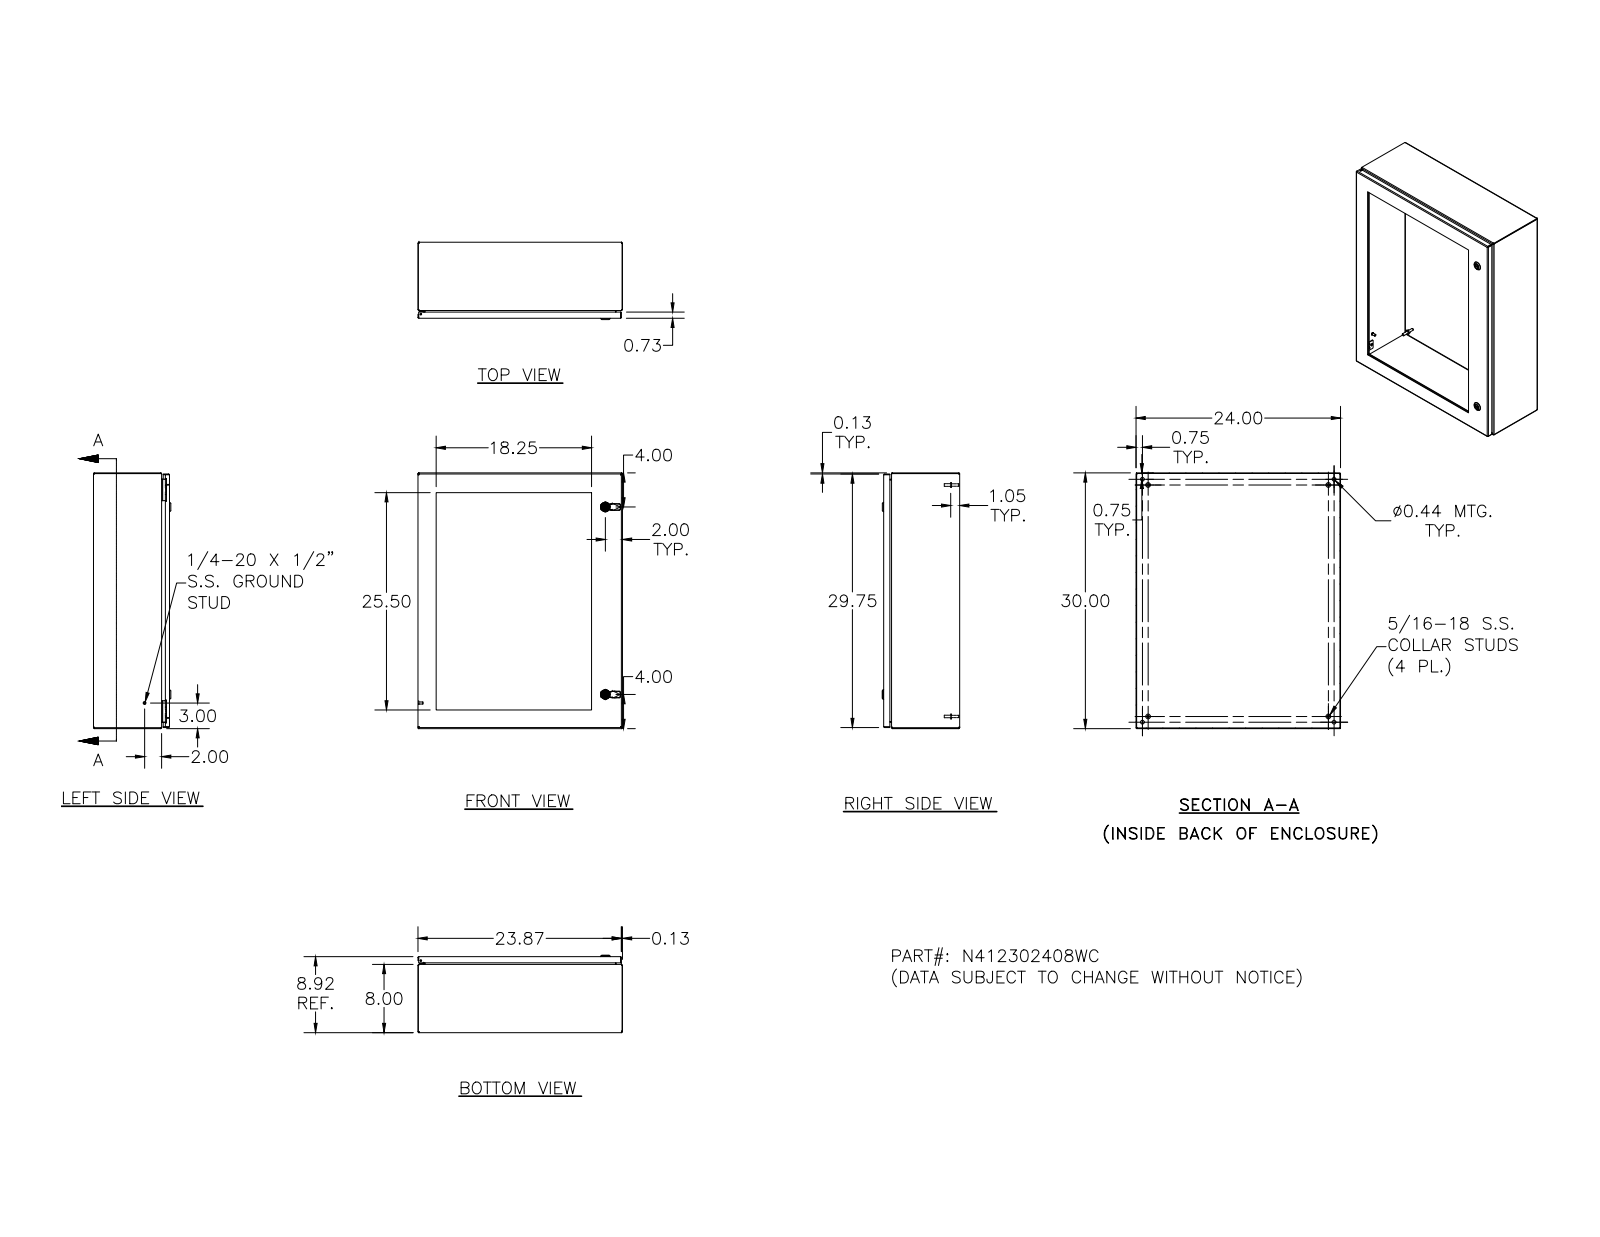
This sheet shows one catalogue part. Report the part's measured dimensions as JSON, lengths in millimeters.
{"part_name": "N412302408WC; N412302408WCBKP; N4123024WCLID; HFW328176 (+8 more)", "step_written_by": "Autodesk Inventor 2011 (AUTOMOTIVE_DESIGN)", "units": "millimeters", "bodies": {"solids": 90, "faces": 2642, "planar": 1017, "cylindrical": 780, "other": 845}, "overall_size": [762, 609.6, 230.5], "volume_mm3": 4708000, "surface_area_mm2": 3497000, "round_holes": [[4, 26], [7.1, 24], [4.8, 5], [2.4, 4], [3.9, 4], [4.2, 4], [4.4, 4], [11.1, 4], [5, 2], [8, 2], [10, 2], [10.2, 2]], "round_bosses_or_shafts": [[8.6, 24], [4.8, 24], [6.4, 10], [14.3, 4], [9.1, 4], [8.1, 4], [7.6, 4], [7, 4]], "partial_cylinders_radius": [[0.3, 54], [0.8, 34], [1.3, 26], [2.7, 24], [0.5, 23], [0.4, 18], [3.2, 16], [0.8, 8]], "face_to_face_distances": [1.9, 224.6, 222.7, 6.4, 218.3, 216.4, 607.7, 760.1, 226.5, 8.2], "hole_center_spacings": [101.6, 203.2, 304.8, 687, 660.4, 709.2, 406.4, 679.5]}
